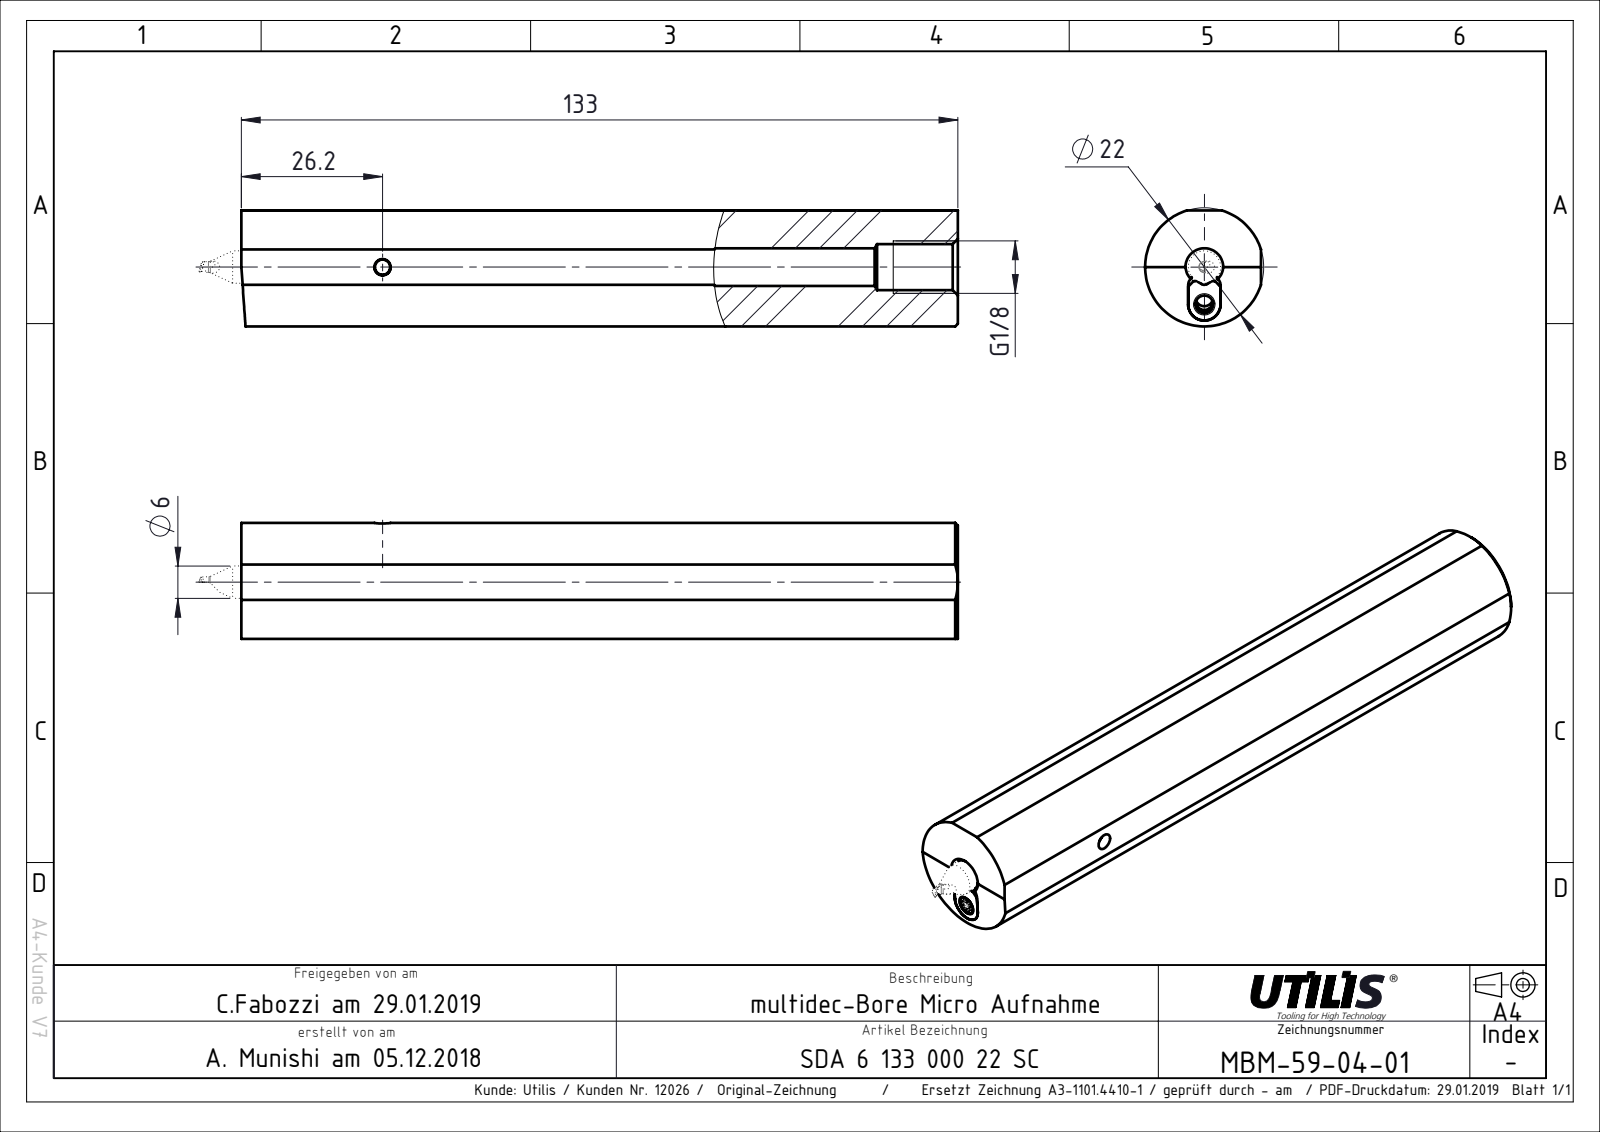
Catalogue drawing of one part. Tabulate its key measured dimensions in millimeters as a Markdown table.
| quantity | value |
| --- | --- |
| part name | MBM-59-04-01 |
| STEP written by | SolidWorks 2018 (CONFIG_CONTROL_DESIGN) |
| units | millimeters |
| bodies | 1 solid, 41 faces (8 planar, 17 cylindrical, 16 other) |
| overall size | 133 × 21.5 × 21.5 |
| volume | 44 191 mm³ |
| surface area | 13 055 mm² |
| round holes (diameter × count) | 3 × 1, 3.3 × 1, 6 × 1, 7 × 1, 8.57 × 1 |
| round bosses / shafts (diameter × count) | 22 × 1 |
| partial cylindrical surfaces (radius × count) | 3 × 1 |
| main face-to-face distances | 133, 13.5, 6, 7.5, 8.8 |
